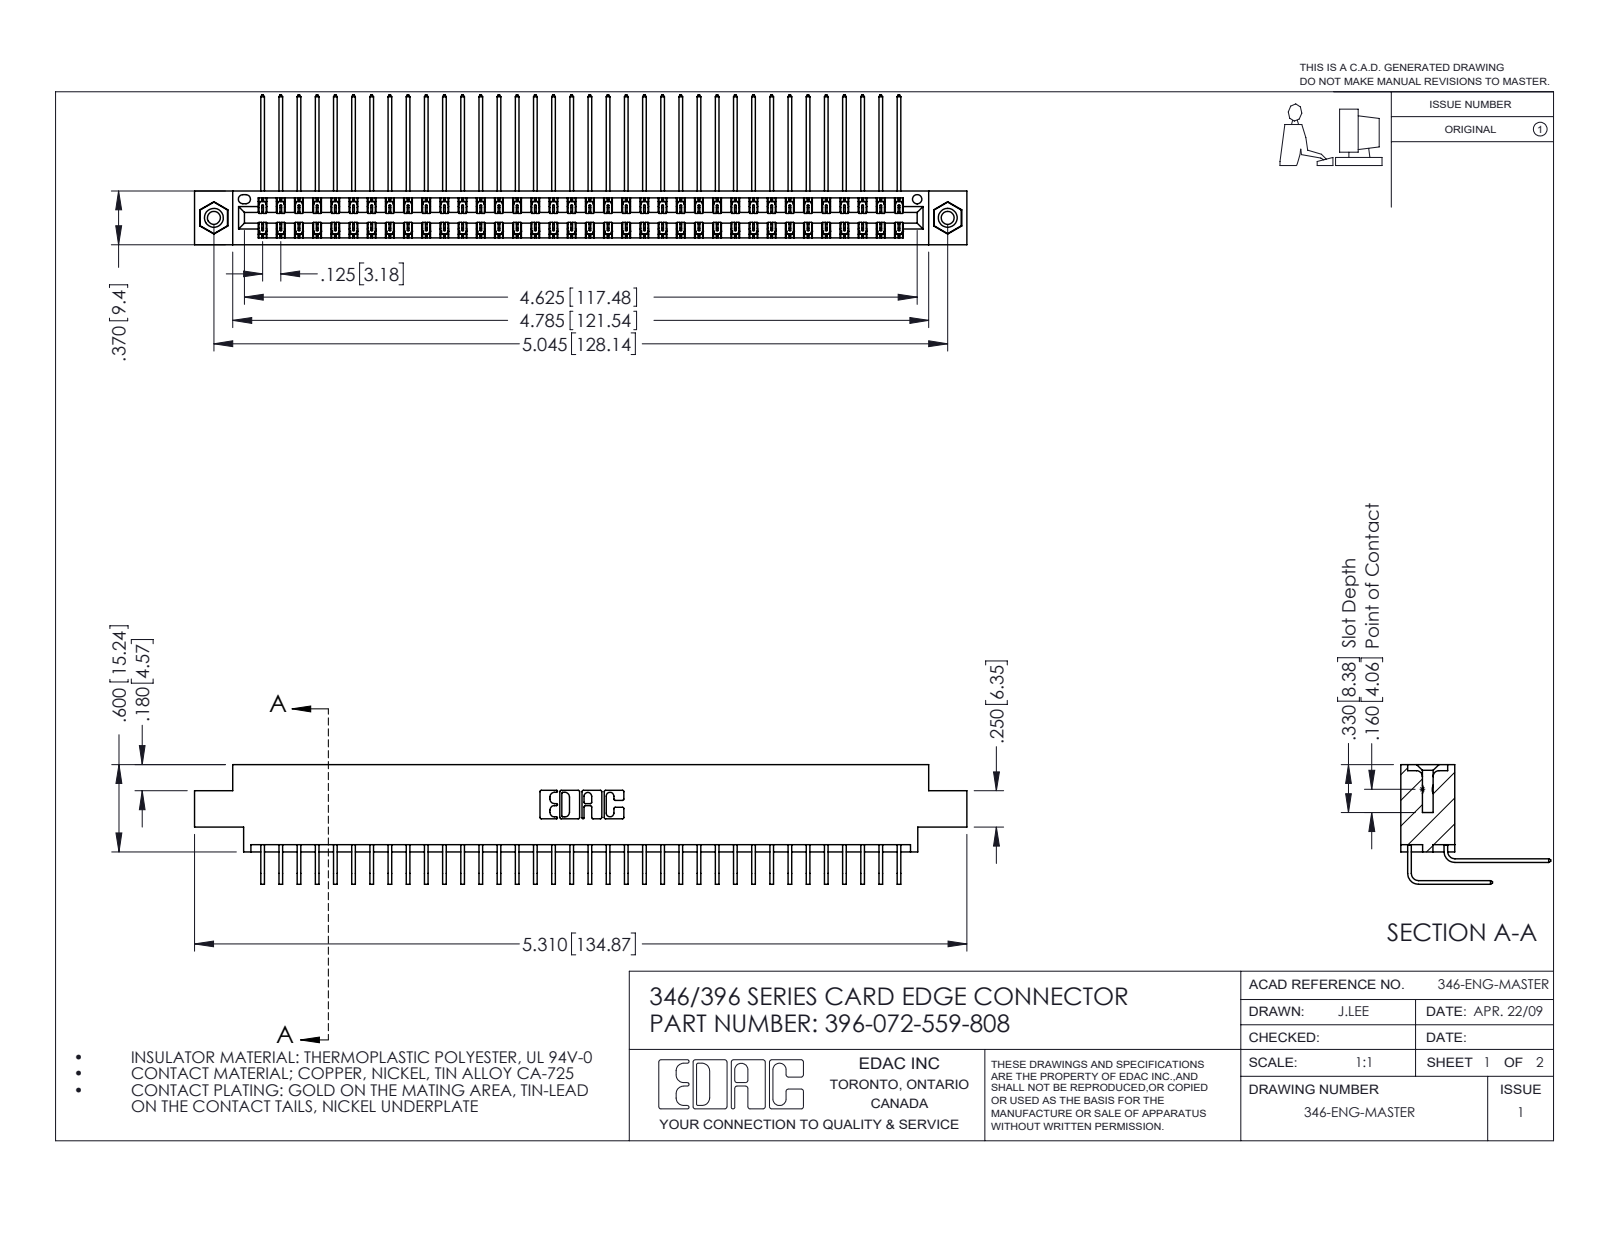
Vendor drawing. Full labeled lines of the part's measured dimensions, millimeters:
Part name (STEP PRODUCT): 396-072-559-808; 345-292-001_558 559 Tail - 1; 345-292-001_559 Tail - 2; 345-250-001_345-250-003-102 (+1 more)
STEP written by: SolidWorks 2016 (CONFIG_CONTROL_DESIGN)
Units: millimetres
Bodies: 75 solids, 4074 faces (2776 planar, 1282 cylindrical, 16 other)
Overall size (bounding box): 134.9 × 26.2 × 20.9
Volume: 13 400 mm³ · Surface area: 20 460 mm²
Round holes (diameter × count): ⌀2.3 ×2, ⌀3.2 ×2, ⌀4 ×2, ⌀1.6 ×1
Round bosses / shafts (diameter × count): ⌀3.9 ×2
Partial cylindrical surfaces — rounded edges, fillets, slot ends (radius × count): R0.2 ×108, R0.3 ×22, R0.2 ×6, R0.8 ×6, R0.7 ×3, R0.4 ×2, R0.6 ×2, R0.6 ×2
Main face-to-face distances: 1.2, 8.2, 0.6, 9.4, 6.4, 1.8, 7.6, 7, 5.6, 3.8
Hole centre spacings: 6.2, 122.8, 128.1
